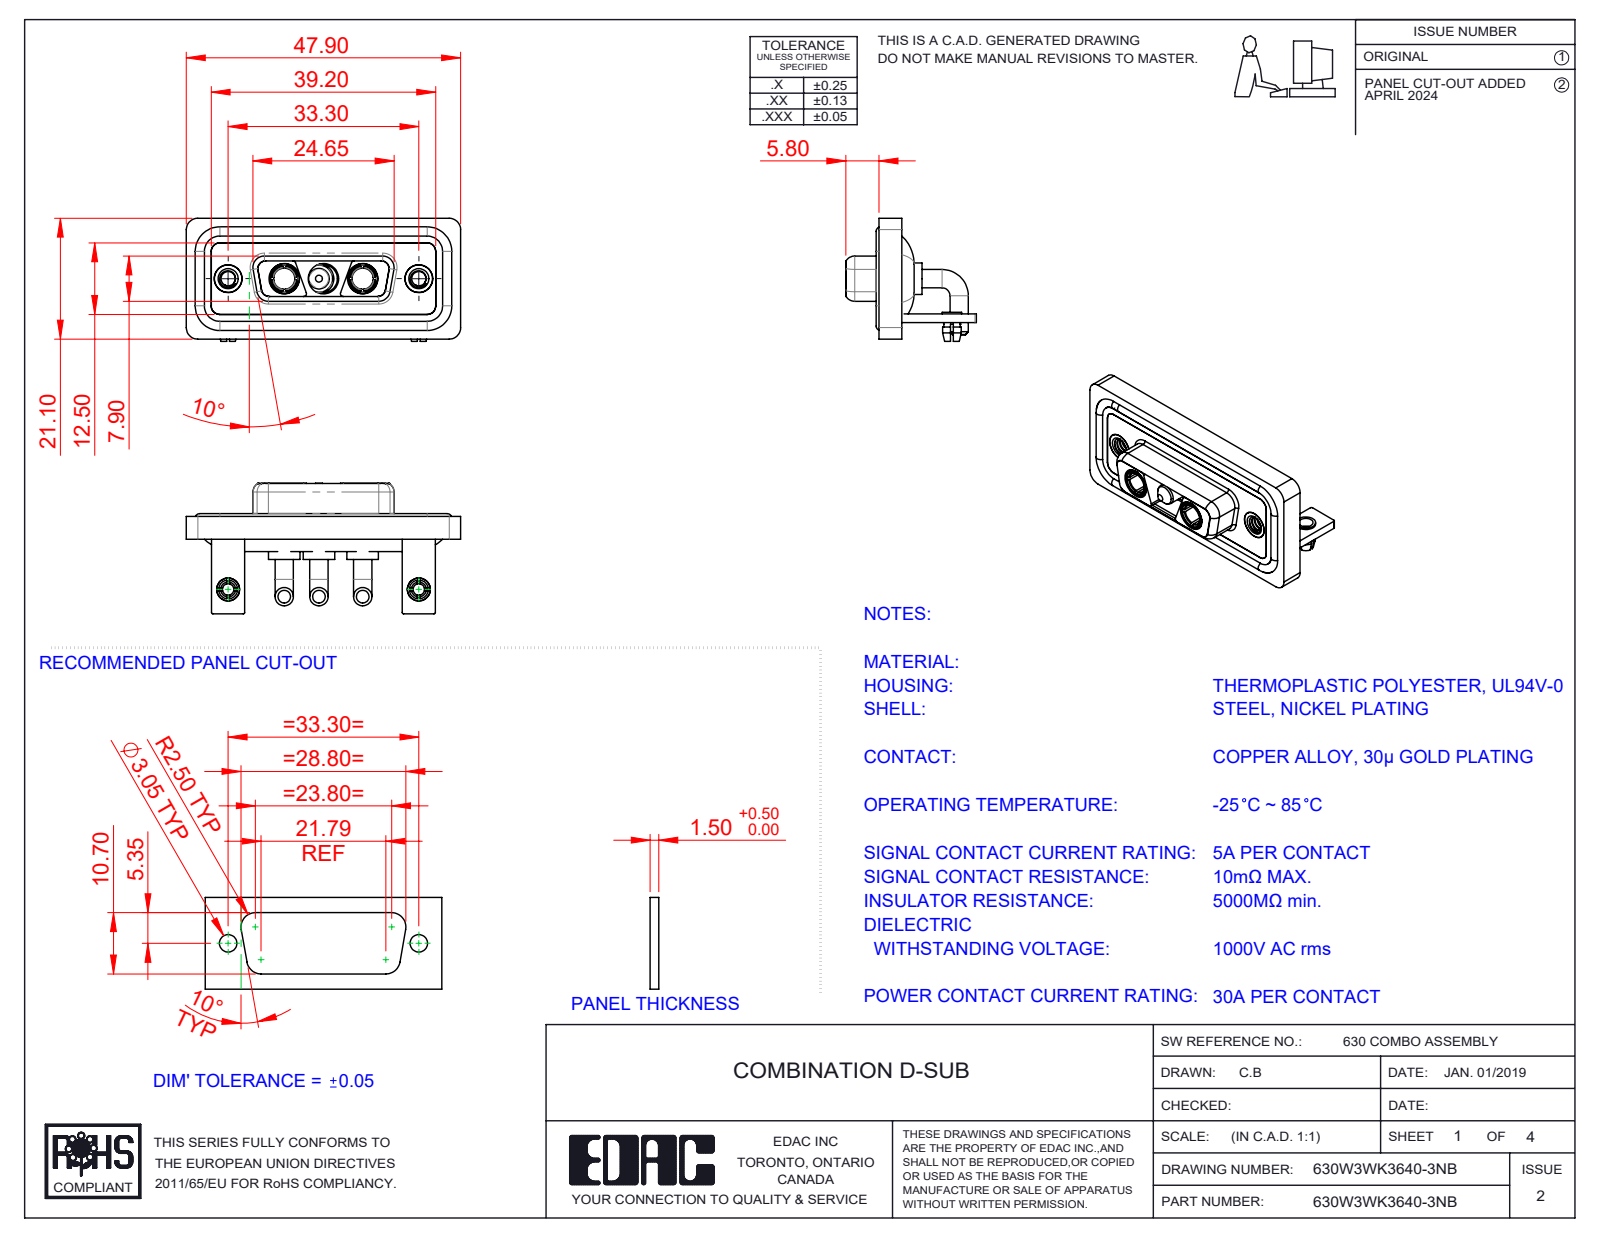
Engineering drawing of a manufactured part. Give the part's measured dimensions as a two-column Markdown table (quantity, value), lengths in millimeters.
| quantity | value |
| --- | --- |
| part name | 630Combo Threaded Rivet_A; 630Combo Stabilizer Bracket_50 Contacts; 630Combo Shell Rear_15 Contacts; Power Pin_30A RA (+6 more) |
| STEP written by | SolidWorks 2023 (CONFIG_CONTROL_DESIGN) |
| units | millimeters |
| bodies | 17 solids, 729 faces (246 planar, 318 cylindrical, 165 other) |
| overall size | 47.9 × 22.8 × 21.5 |
| volume | 6 512 mm³ |
| surface area | 10 743 mm² |
| round holes (diameter × count) | 4.85 × 5, 2.5 × 4, 5.3 × 3, 2 × 2, 3.2 × 2, 3.7 × 2, 4 × 2, 4.05 × 2, 5 × 2 |
| round bosses / shafts (diameter × count) | 3.2 × 6, 1.6 × 4, 5.5 × 3, 5.2 × 3, 4.75 × 3, 3.75 × 3, 4.96 × 2, 4.95 × 2 |
| partial cylindrical surfaces (radius × count) | 2 × 21, 1.5 × 18, 0.25 × 16, 1.35 × 12, 0.5 × 9, 1.6 × 8, 0.6 × 4, 0.65 × 4 |
| main face-to-face distances | 0.4, 2.9, 1.5, 3.7, 1.8, 1.1, 4.1, 1.6, 2.5, 1.4 |
| hole center spacings | 6.85, 9.8, 16.65, 23.5, 33.3, 13.7 |
